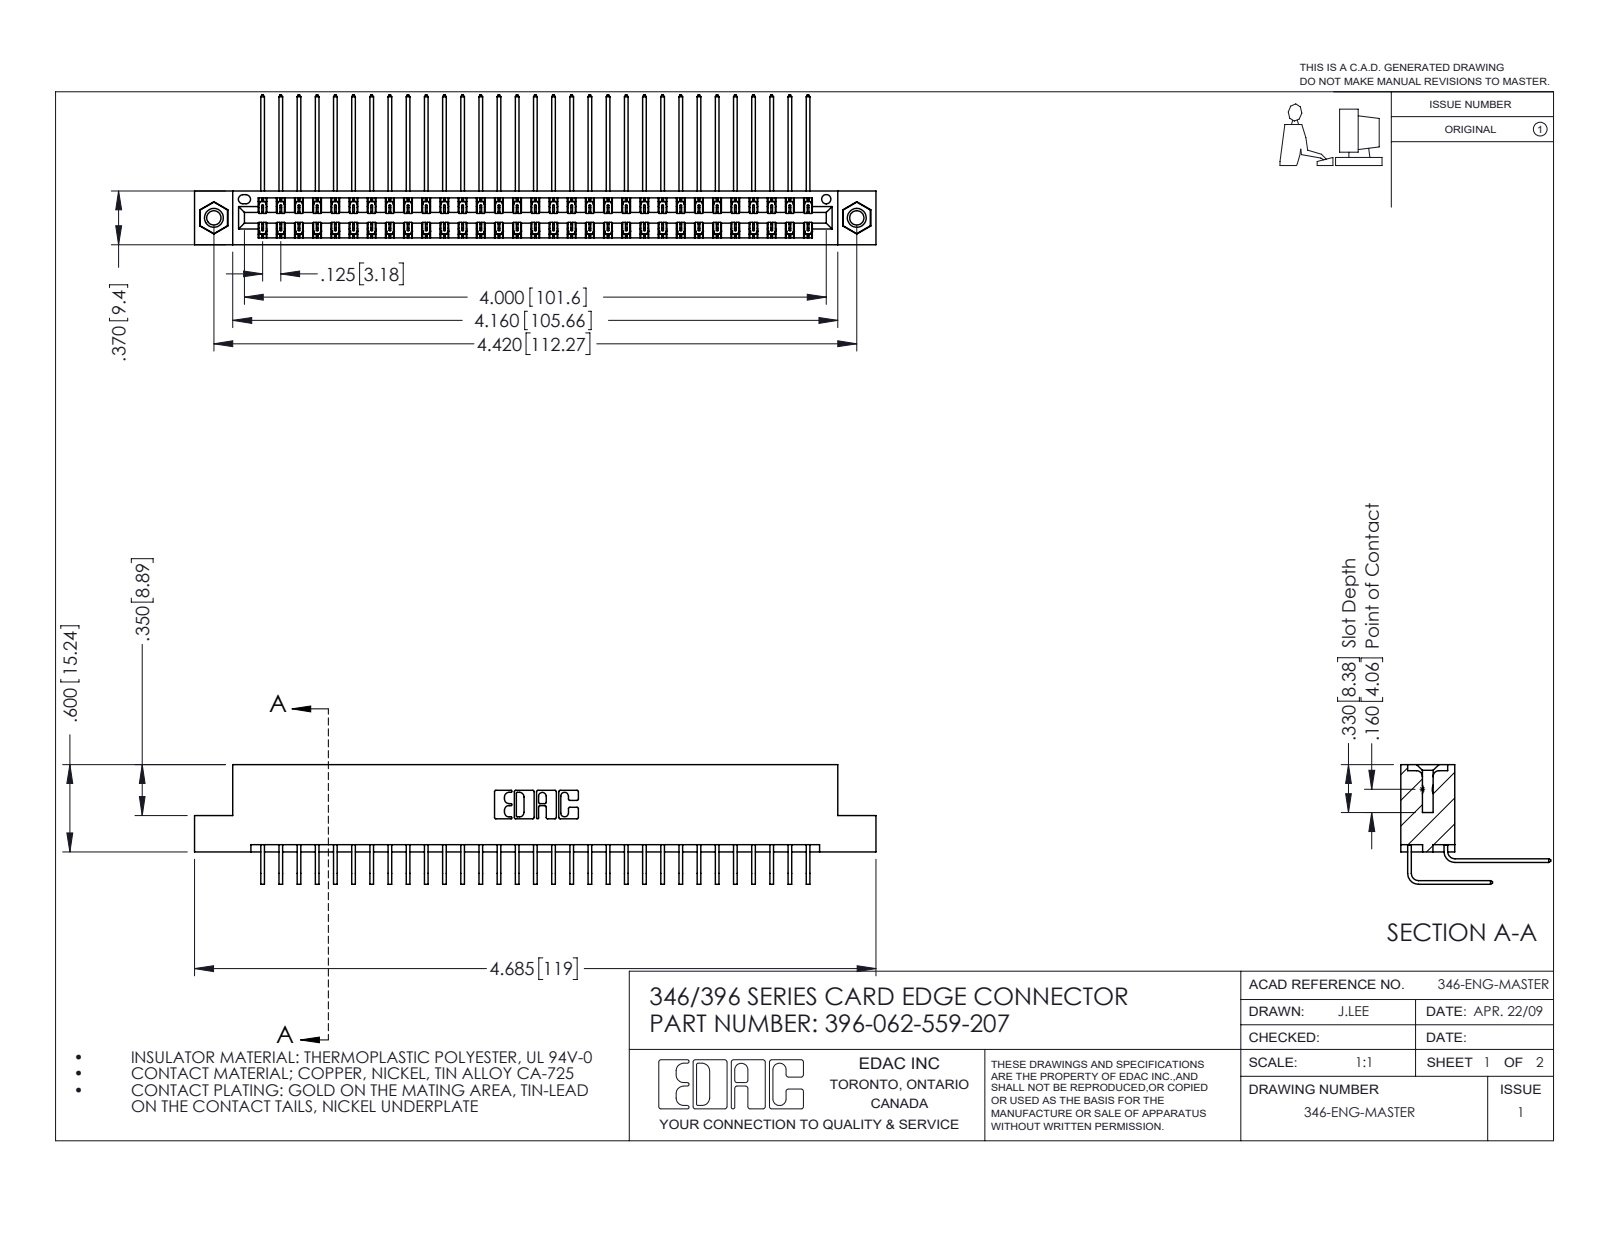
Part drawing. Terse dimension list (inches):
name: 345-250-001_345-250-005-103; 396-062-559-207; 345-292-001_558 559 Tail - 1; 346 Part_Flush Mounting Lugs - 0.156 Dia-TI (+1 more)
written by: SolidWorks 2016 (CONFIG_CONTROL_DESIGN)
unit: in
bodies: 65 solids, 3530 faces (2402 planar, 1112 cylindrical, 16 other)
size: 4.685 × 1.03 × 0.823
volume: 0.724 in³; area: 27.72 in²
holes: 2× ⌀0.098, 2× ⌀0.125, 2× ⌀0.156, 1× ⌀0.064
bosses: 2× ⌀0.155
rounds: 93× R0.006, 22× R0.01, 6× R0.007, 6× R0.031, 3× R0.026, 2× R0.014, 2× R0.022, 2× R0.024
face distances: 0.048, 0.322, 0.025, 0.25, 0.37, 0.072, 0.298, 0.275, 0.148, 0.222
hole spacings: 0.246, 4.212, 4.42
